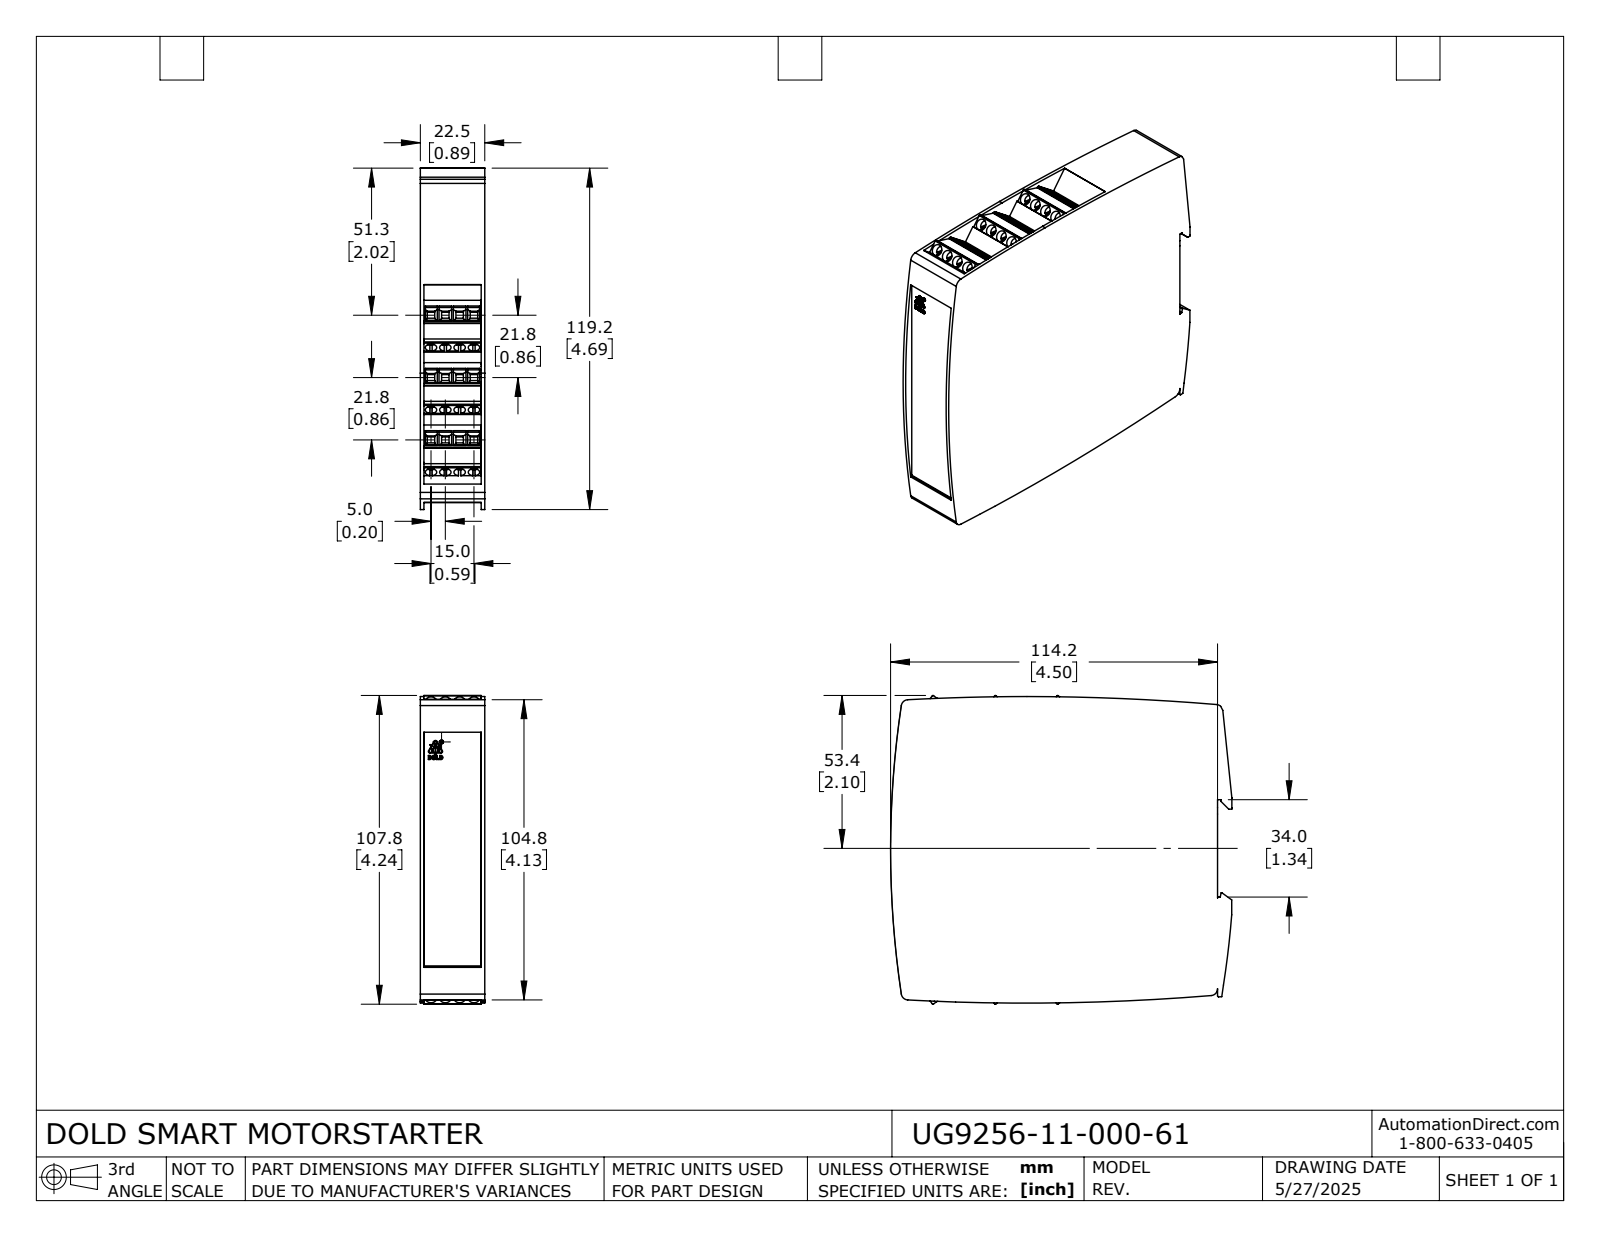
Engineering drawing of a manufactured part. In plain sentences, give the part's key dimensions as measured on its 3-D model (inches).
The part is named "UG9256-11-000-61". Its 3-D file was written by "SolidWorks 2024 (AUTOMOTIVE_DESIGN)". It is 1 solid with 1036 faces: 813 planar, 222 cylindrical and 1 other. Overall it measures 4.693 by 4.243 by 0.886 inches. Its volume is 15.85 cubic inches and its surface area 64.72 square inches. Round holes: 24 of diameter 0.157, 1 of diameter 0.053. Round bosses or shafts: 24 of diameter 0.15, 1 of diameter 0.049. Partial cylindrical surfaces (rounded edges, fillets, slot ends): 15 of radius 0.012, 14 of radius 0.02, 12 of radius 0.004, 7 of radius 0.094, 6 of radius 0.005, 4 of radius 0.004, 4 of radius 31.496, 3 of radius 0.021. The main face-to-face distances are 0.886, 0.049, 0.837, 0.675, 4.379, 0.051, 0.835, 1.35, 0.528, 0.785. The hole center spacings are 0.563, 0.197, 0.528, 0.658, 0.394, 1.073, 0.792, 1.055.
